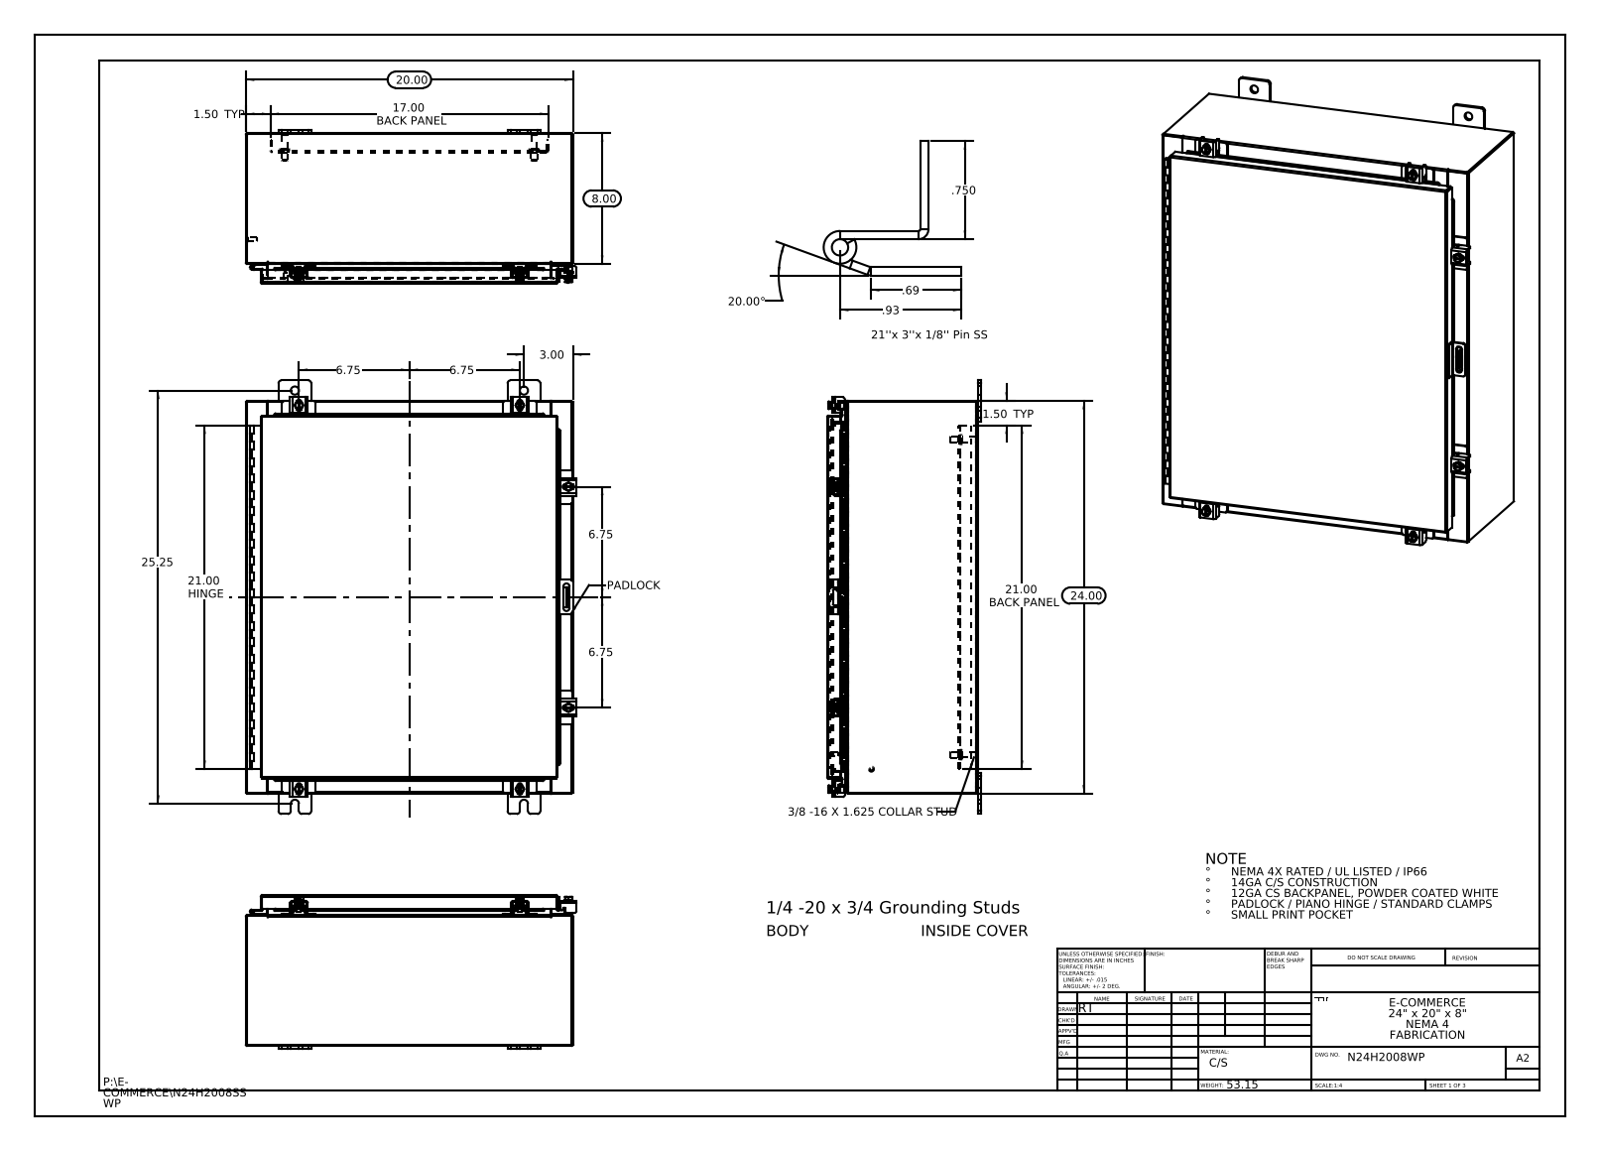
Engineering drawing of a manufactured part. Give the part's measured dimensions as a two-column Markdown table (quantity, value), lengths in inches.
| quantity | value |
| --- | --- |
| part name | N24H2008SSWP 22101002; N24H2008SSWP Clamp Bracket; N24H2008SSWP Padlock Staple; N24H2008SSWP Padlock Hasp (+8 more) |
| STEP written by | SolidWorks 2013 (CONFIG_CONTROL_DESIGN) |
| units | inches |
| bodies | 49 solids, 1735 faces (914 planar, 713 cylindrical, 108 other) |
| overall size | 26.5 × 20.211 × 9.389 |
| volume | 187 in³ |
| surface area | 4 713 in² |
| round holes (diameter × count) | 0.5 × 8, 0.213 × 6, 0.26 × 6, 0.125 × 2 |
| round bosses / shafts (diameter × count) | 0.25 × 7, 0.5 × 6, 0.399 × 6, 0.625 × 4, 0.375 × 4, 0.33 × 4, 0.315 × 2, 0.236 × 2 |
| partial cylindrical surfaces (radius × count) | 0.06 × 30, 0.013 × 25, 0.19 × 24, 0.088 × 21, 0.12 × 12, 0.141 × 12, 0.125 × 10, 0.05 × 9 |
| main face-to-face distances | 0.075, 9.126, 9.051, 9.201, 0.104, 19.925, 1, 1.075, 8.051, 8.126 |
| hole center spacings | 21.369, 25.739, 13.5, 0.431, 0.934, 1.858, 2.275, 2.276 |
